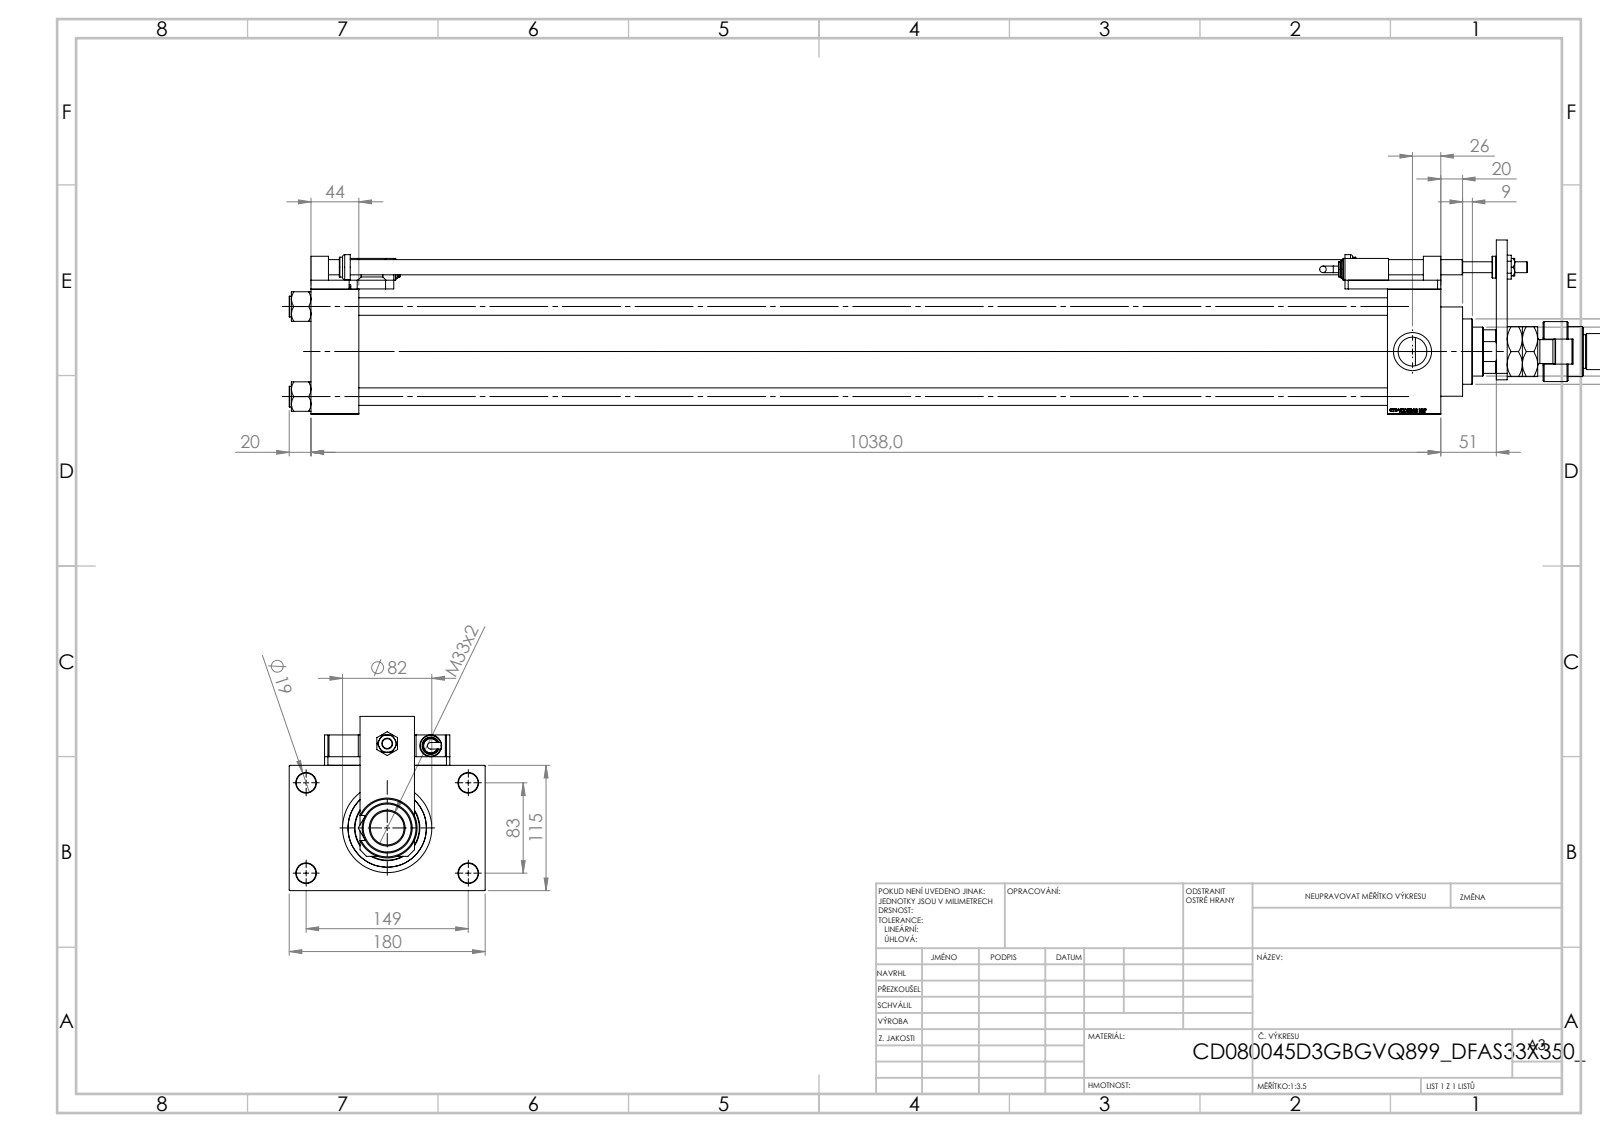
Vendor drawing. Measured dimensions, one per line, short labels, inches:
name: V215CD_VCP_D; Zatka_pro_OIL_PORT; V215CD_SWITCH_Q_ZARAZKA; V215CD_VC_A (+7 more)
written by: SolidWorks 2019 (CONFIG_CONTROL_DESIGN)
unit: in
bodies: 28 solids, 1565 faces (742 planar, 180 cylindrical, 643 other)
size: 48.858 × 7.087 × 6.299
volume: 327.8 in³; area: 1 905 in²
holes: 4× ⌀0.335, 4× ⌀0.531, 4× ⌀0.63, 4× ⌀0.709, 4× ⌀1.041, 4× ⌀1.378, 3× ⌀0.276, 1× ⌀0.394, 1× ⌀0.551, 1× ⌀1.24, 1× ⌀1.299, 1× ⌀1.535
bosses: 4× ⌀0.748, 3× ⌀0.787, 2× ⌀0.63, 2× ⌀0.551, 2× ⌀0.236, 1× ⌀3.386, 1× ⌀3.228, 1× ⌀2.362
rounds: 4× R0.295, 1× R0.453, 1× R0.866
face distances: 4.528, 0.315, 1.732, 1.929, 39.134, 40.866, 38.937, 37.205, 4.843, 1.28
hole spacings: 1.305, 2.302, 3.256, 3.357, 3.513, 4.561, 5.607, 0.837
